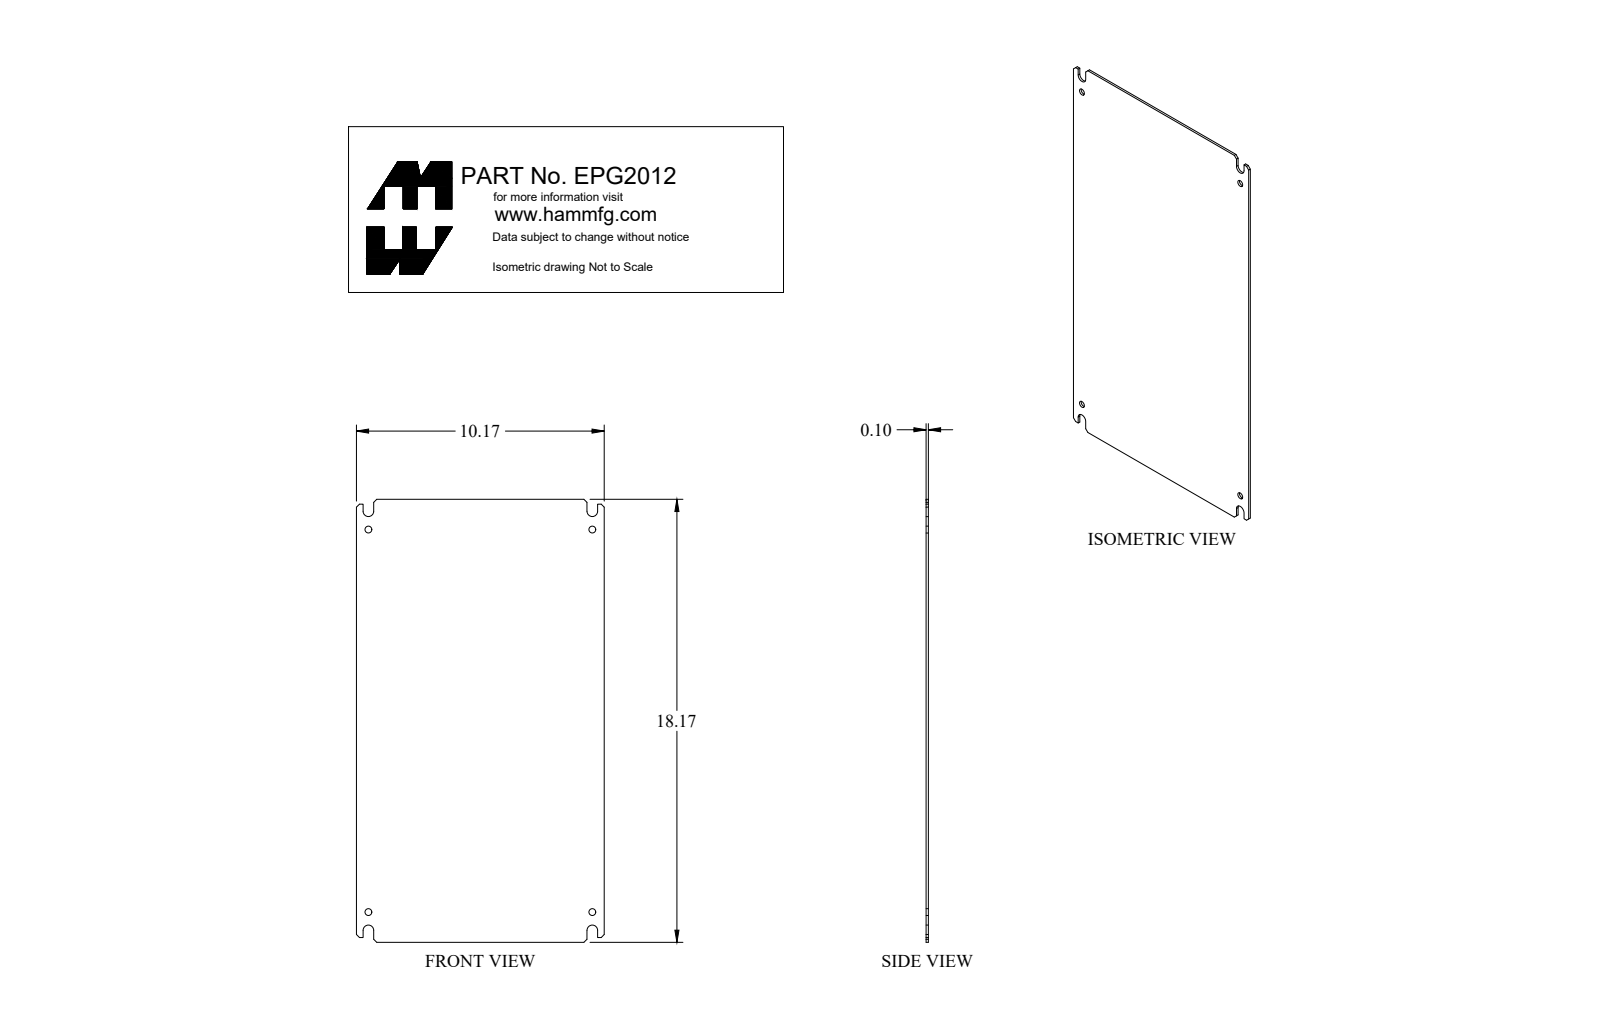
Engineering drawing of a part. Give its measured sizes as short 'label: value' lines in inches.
name: EPG2012
written by: SolidWorks 2018 (AUTOMOTIVE_DESIGN)
unit: in
bodies: 1 solid, 40 faces (26 planar, 14 cylindrical, 0 other)
size: 18.17 × 10.17 × 0.095
volume: 17.4 in³; area: 372.2 in²
holes: 4× ⌀0.281
rounds: 4× R0.219
face distances: 0.095, 10.17, 18.17, 0.709, 9.461, 0.272, 9.898, 0.437, 9.188, 8.751
hole spacings: 9.188, 15.688, 18.181
